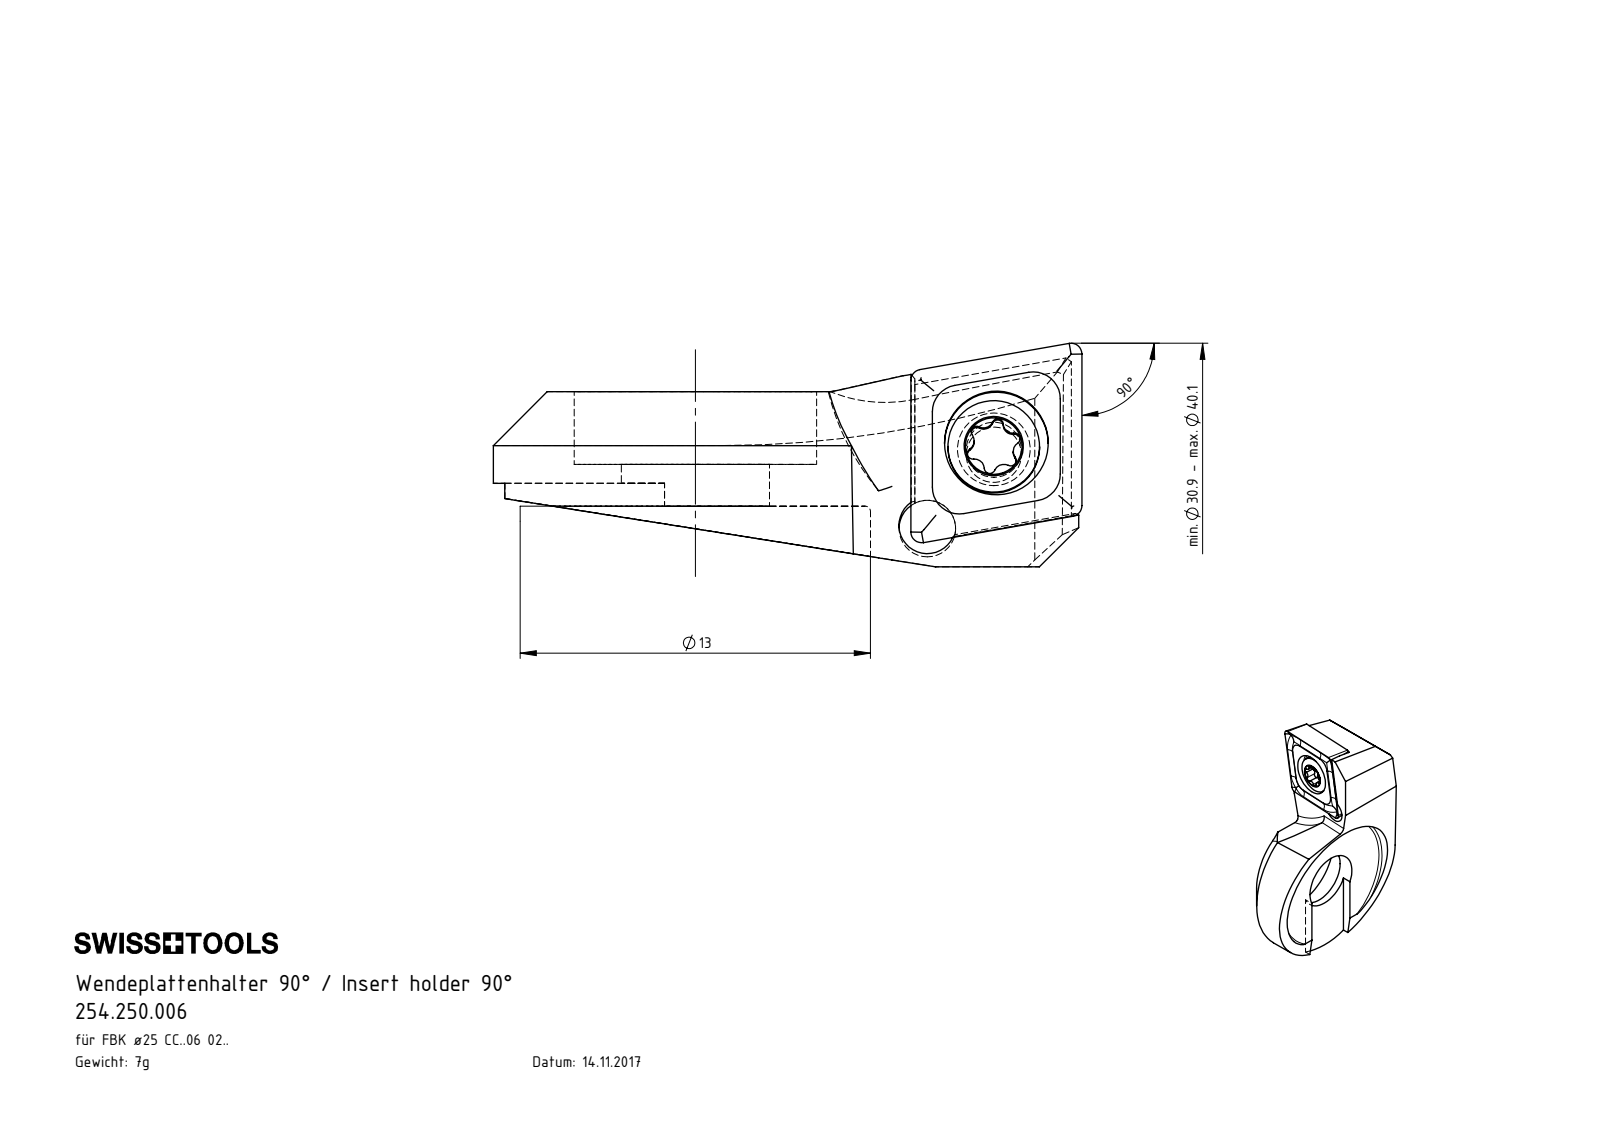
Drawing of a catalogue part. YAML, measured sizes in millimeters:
part_name: "WCA-ER2.001.006_A; CCMT060204; F25.WCA.001.006; F25-WCA.001.006_D_fertigbearbeitet"
step_written_by: "SolidWorks 2017 (AUTOMOTIVE_DESIGN)"
units: millimeters
bodies: {solids: 3, faces: 103, planar: 39, cylindrical: 26, other: 38}
overall_size: [21.85, 15, 8.3]
volume: 783
surface_area: 1050
round_holes:
  - {diameter: 2.05, count: 1}
  - {diameter: 2.1, count: 1}
  - {diameter: 2.8, count: 1}
  - {diameter: 3.85, count: 1}
  - {diameter: 5.5, count: 1}
  - {diameter: 9, count: 1}
round_bosses_or_shafts:
  - {diameter: 3.4, count: 1}
  - {diameter: 2.5, count: 1}
partial_cylinders:
  - {radius: 0.21, count: 6}
  - {radius: 0.36, count: 5}
  - {radius: 0.5, count: 2}
  - {radius: 0.36, count: 1}
  - {radius: 6.4, count: 1}
  - {radius: 6.5, count: 1}
  - {radius: 7.5, count: 1}
  - {radius: 9, count: 1}
face_to_face_distances: [1.55, 2.7, 4.25, 3.4, 0.7, 0.85, 6.5, 3.8, 3.1, 2.25]
hole_center_spacings: [3.84, 3.99]
